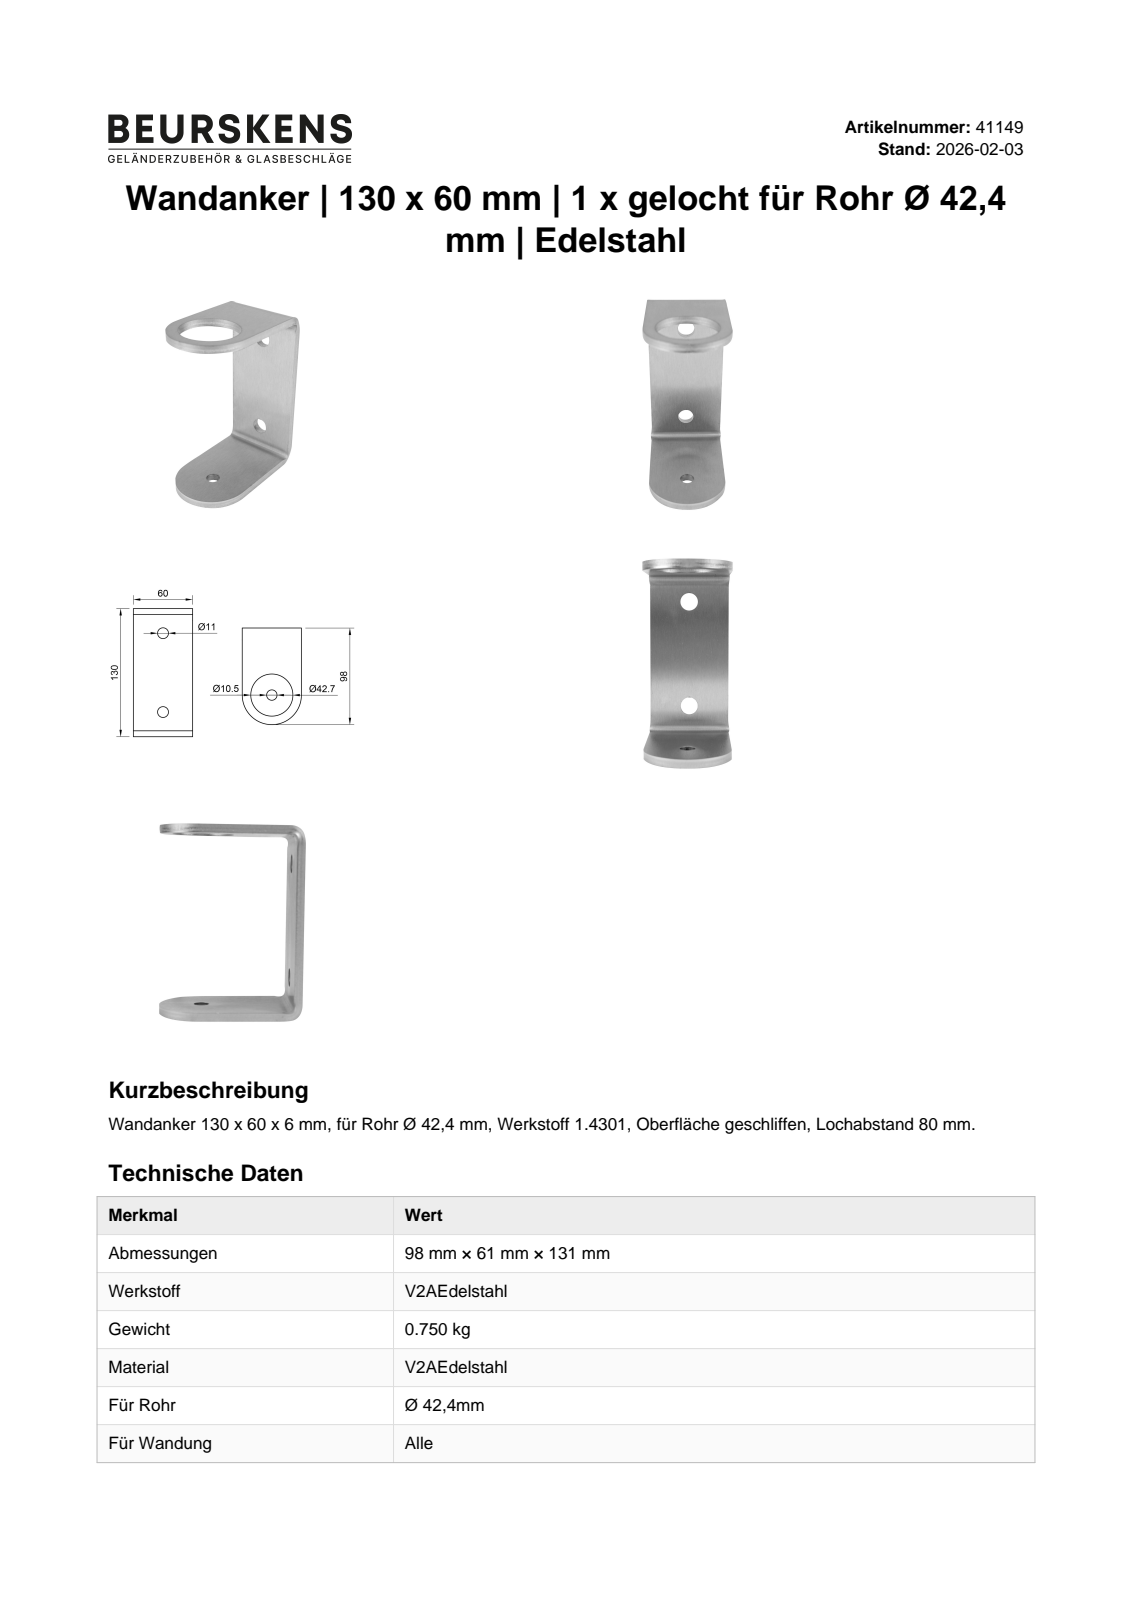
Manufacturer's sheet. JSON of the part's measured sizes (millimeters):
{"part_name": "41149", "step_written_by": "Autodesk Inventor 2022 (AUTOMOTIVE_DESIGN)", "units": "millimeters", "bodies": {"solids": 1, "faces": 26, "planar": 16, "cylindrical": 10, "other": 0}, "overall_size": [130, 98, 60], "volume_mm3": 95371, "surface_area_mm2": 37294, "round_holes": [[11, 2], [10.5, 1], [42.7, 1]], "partial_cylinders_radius": [[6, 2], [12, 2], [30, 1]], "face_to_face_distances": [6, 124, 130, 118, 60], "hole_center_spacings": [80]}
